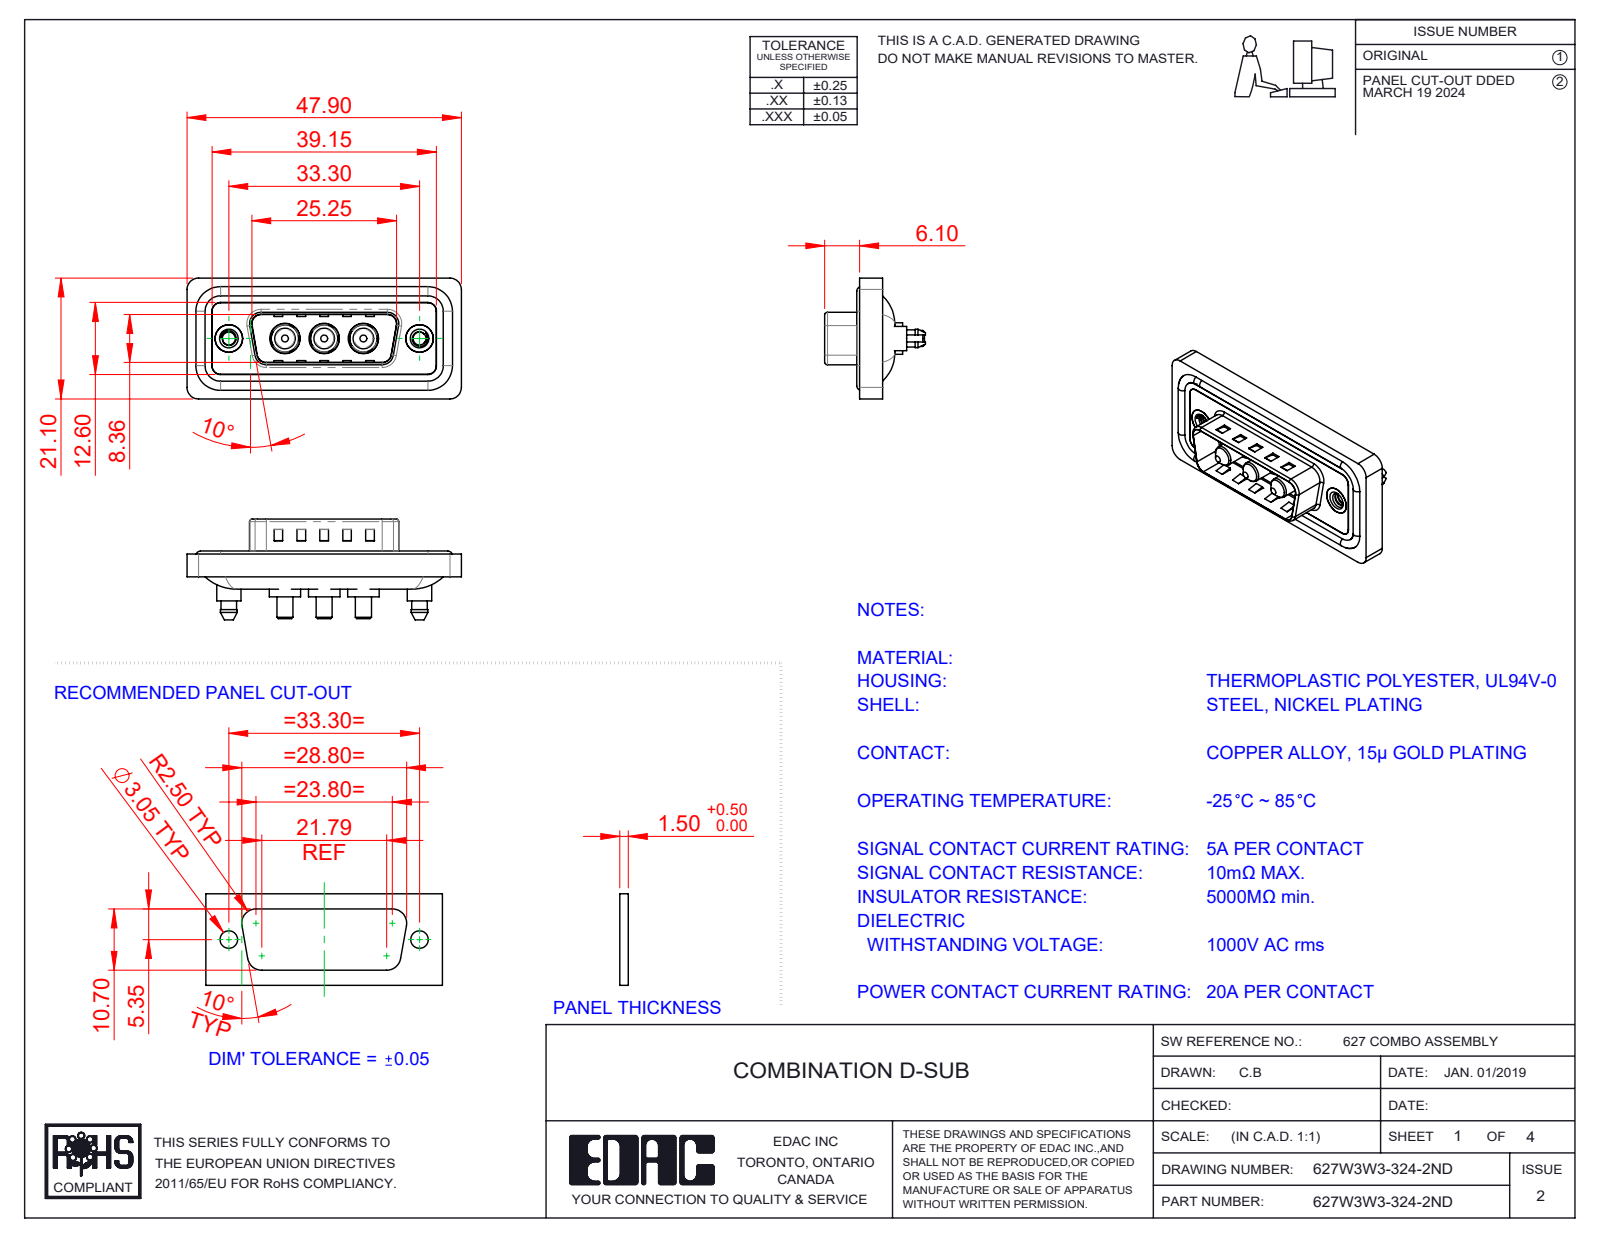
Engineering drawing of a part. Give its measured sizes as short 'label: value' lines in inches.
name: 627Combo Threaded Boardlock_5; 627Combo Shell Front_15 Contacts; 627Combo Waterproof Housing_15 Contacts; Power Pin_20A S (+4 more)
written by: SolidWorks 2023 (CONFIG_CONTROL_DESIGN)
unit: in
bodies: 13 solids, 622 faces (223 planar, 281 cylindrical, 118 other)
size: 1.886 × 0.831 × 0.693
volume: 0.349 in³; area: 14.09 in²
holes: 3× ⌀0.191, 3× ⌀0.209, 2× ⌀0.089, 2× ⌀0.157, 2× ⌀0.189, 2× ⌀0.197
bosses: 4× ⌀0.063, 3× ⌀0.217, 3× ⌀0.205, 3× ⌀0.187, 3× ⌀0.148, 3× ⌀0.142, 3× ⌀0.11, 2× ⌀0.213
rounds: 28× R0.059, 20× R0.079, 10× R0.063, 8× R0.02, 4× R0.01, 4× R0.024, 4× R0.026, 4× R0.035
face distances: 0.016, 0.043, 0.059, 0.122, 0.063, 0.02, 0.114, 0.157, 0.028, 0.032
hole spacings: 0.27, 0.386, 0.656, 0.925, 0.539, 1.311
